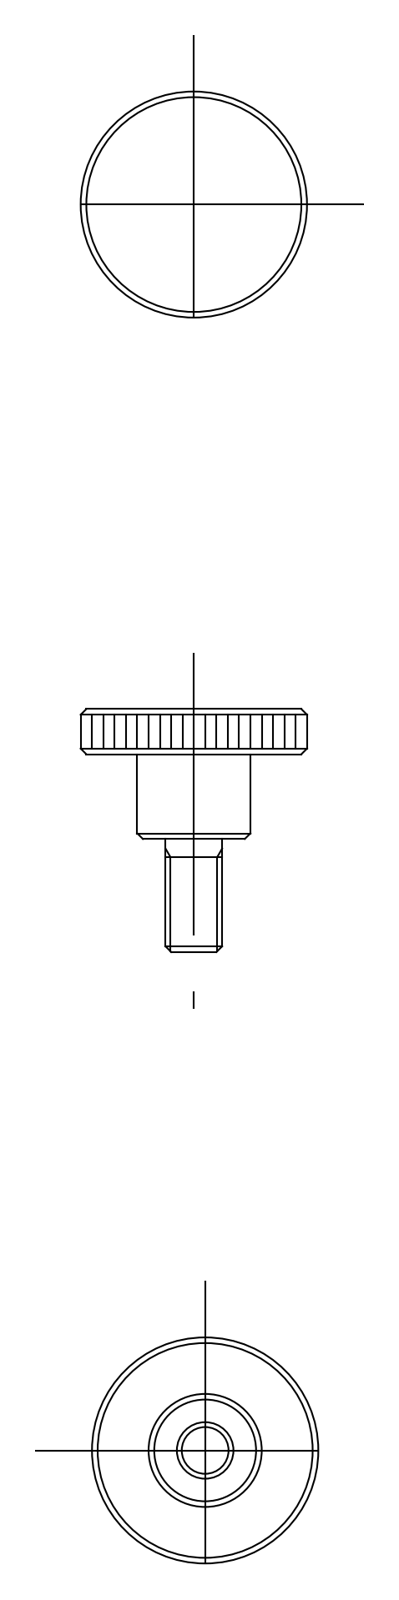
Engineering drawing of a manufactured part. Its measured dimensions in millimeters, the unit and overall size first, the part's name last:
Units: millimetres
Overall size (bounding box): 21.5 × 20 × 20
Volume: 2 024 mm³ · Surface area: 1 221 mm²
Bodies: 1 solid, 18 faces (0 planar, 0 cylindrical, 18 other)
Part name (STEP PRODUCT): knob
STEP written by: CADfix (AUTOMOTIVE_DESIGN)
